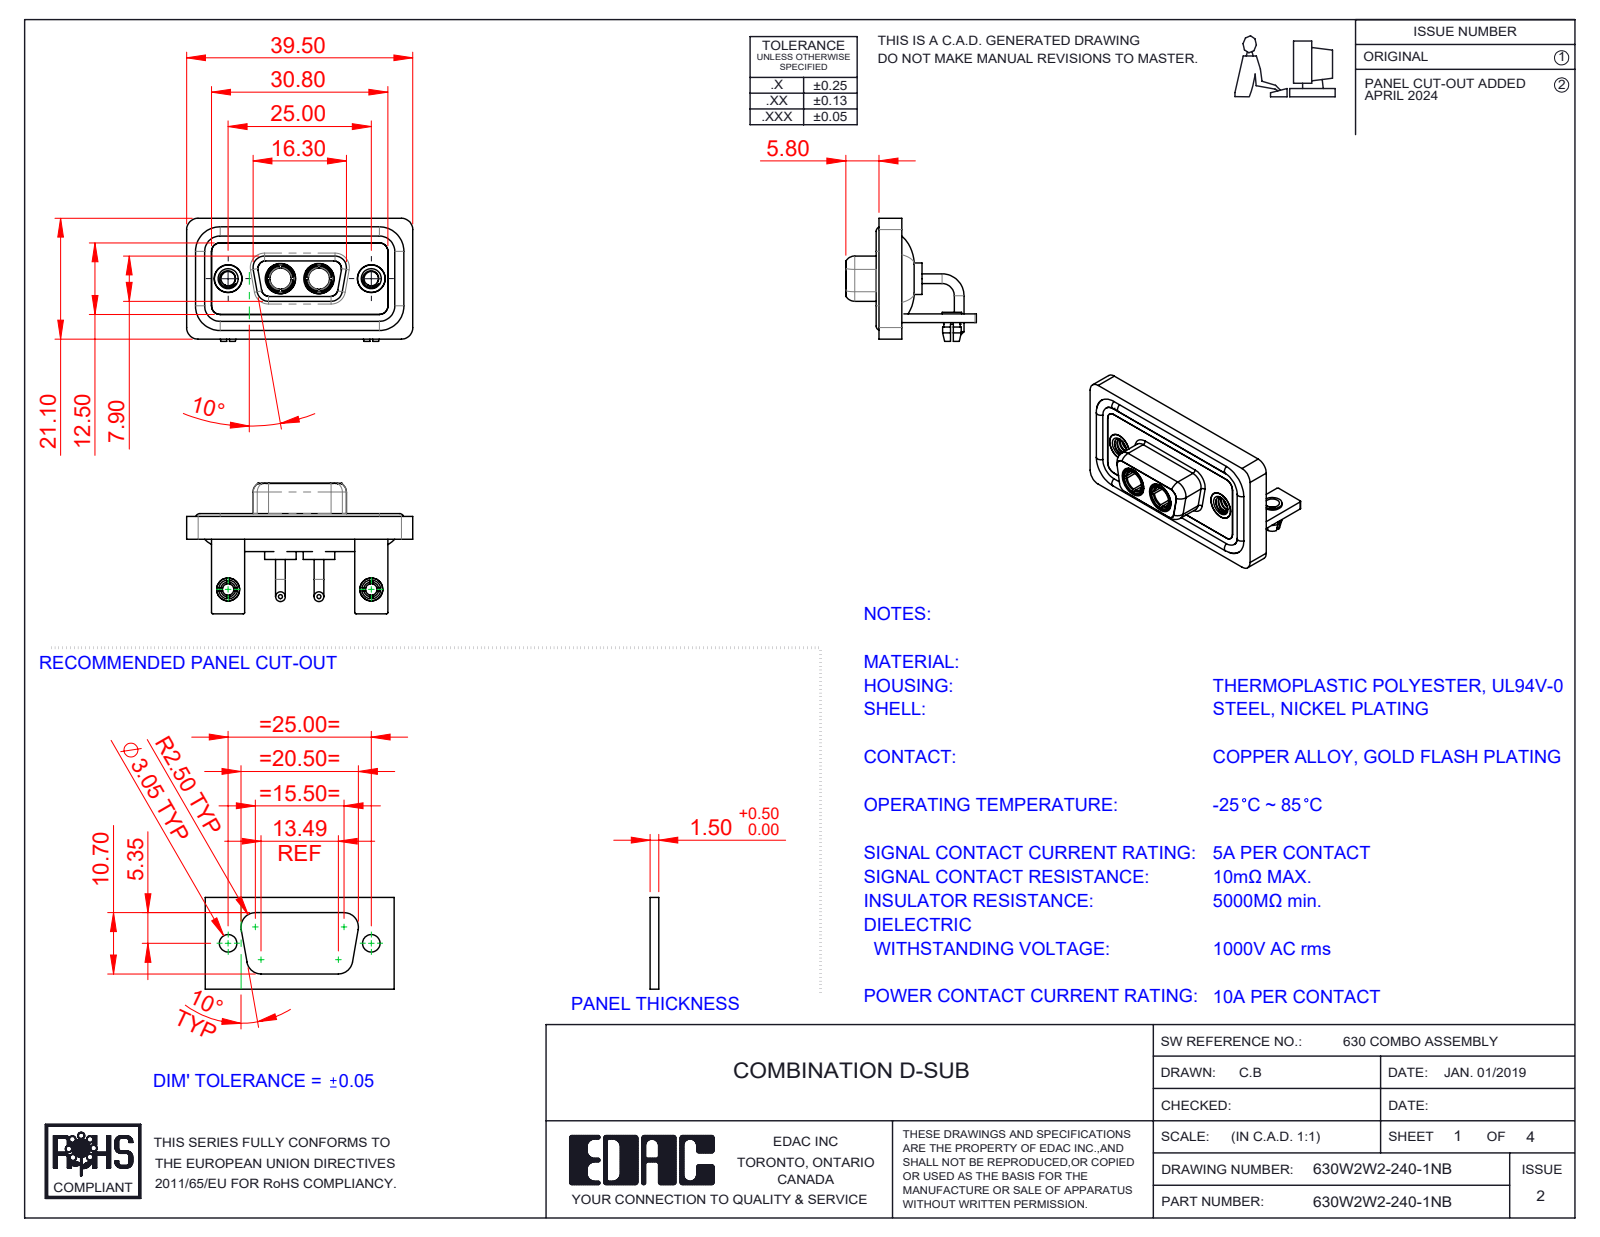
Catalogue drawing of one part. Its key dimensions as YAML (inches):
part_name: "630Combo Waterproof Housing_09 Contacts; 630W2W2-140-1NB; 630Combo Threaded Rivet_A; 630Combo Housing_2W2 (+5 more)"
step_written_by: "SolidWorks 2023 (CONFIG_CONTROL_DESIGN)"
units: inches
bodies: {solids: 15, faces: 676, planar: 231, cylindrical: 292, other: 153}
overall_size: [1.555, 0.898, 0.846]
volume: 0.311
surface_area: 13.38
round_holes:
  - {diameter: 0.098, count: 4}
  - {diameter: 0.191, count: 4}
  - {diameter: 0.079, count: 2}
  - {diameter: 0.126, count: 2}
  - {diameter: 0.146, count: 2}
  - {diameter: 0.157, count: 2}
  - {diameter: 0.159, count: 2}
  - {diameter: 0.197, count: 2}
  - {diameter: 0.209, count: 2}
round_bosses_or_shafts:
  - {diameter: 0.067, count: 4}
  - {diameter: 0.063, count: 4}
  - {diameter: 0.217, count: 2}
  - {diameter: 0.205, count: 2}
  - {diameter: 0.195, count: 2}
  - {diameter: 0.195, count: 2}
  - {diameter: 0.189, count: 2}
  - {diameter: 0.187, count: 2}
partial_cylinders:
  - {radius: 0.079, count: 19}
  - {radius: 0.059, count: 18}
  - {radius: 0.01, count: 16}
  - {radius: 0.053, count: 8}
  - {radius: 0.063, count: 8}
  - {radius: 0.02, count: 5}
  - {radius: 0.024, count: 4}
  - {radius: 0.026, count: 4}
face_to_face_distances: [0.016, 0.114, 0.059, 0.071, 0.043, 0.146, 0.031, 0.098, 0.063, 0.122]
hole_center_spacings: [0.36, 0.624, 0.984, 0.265]
